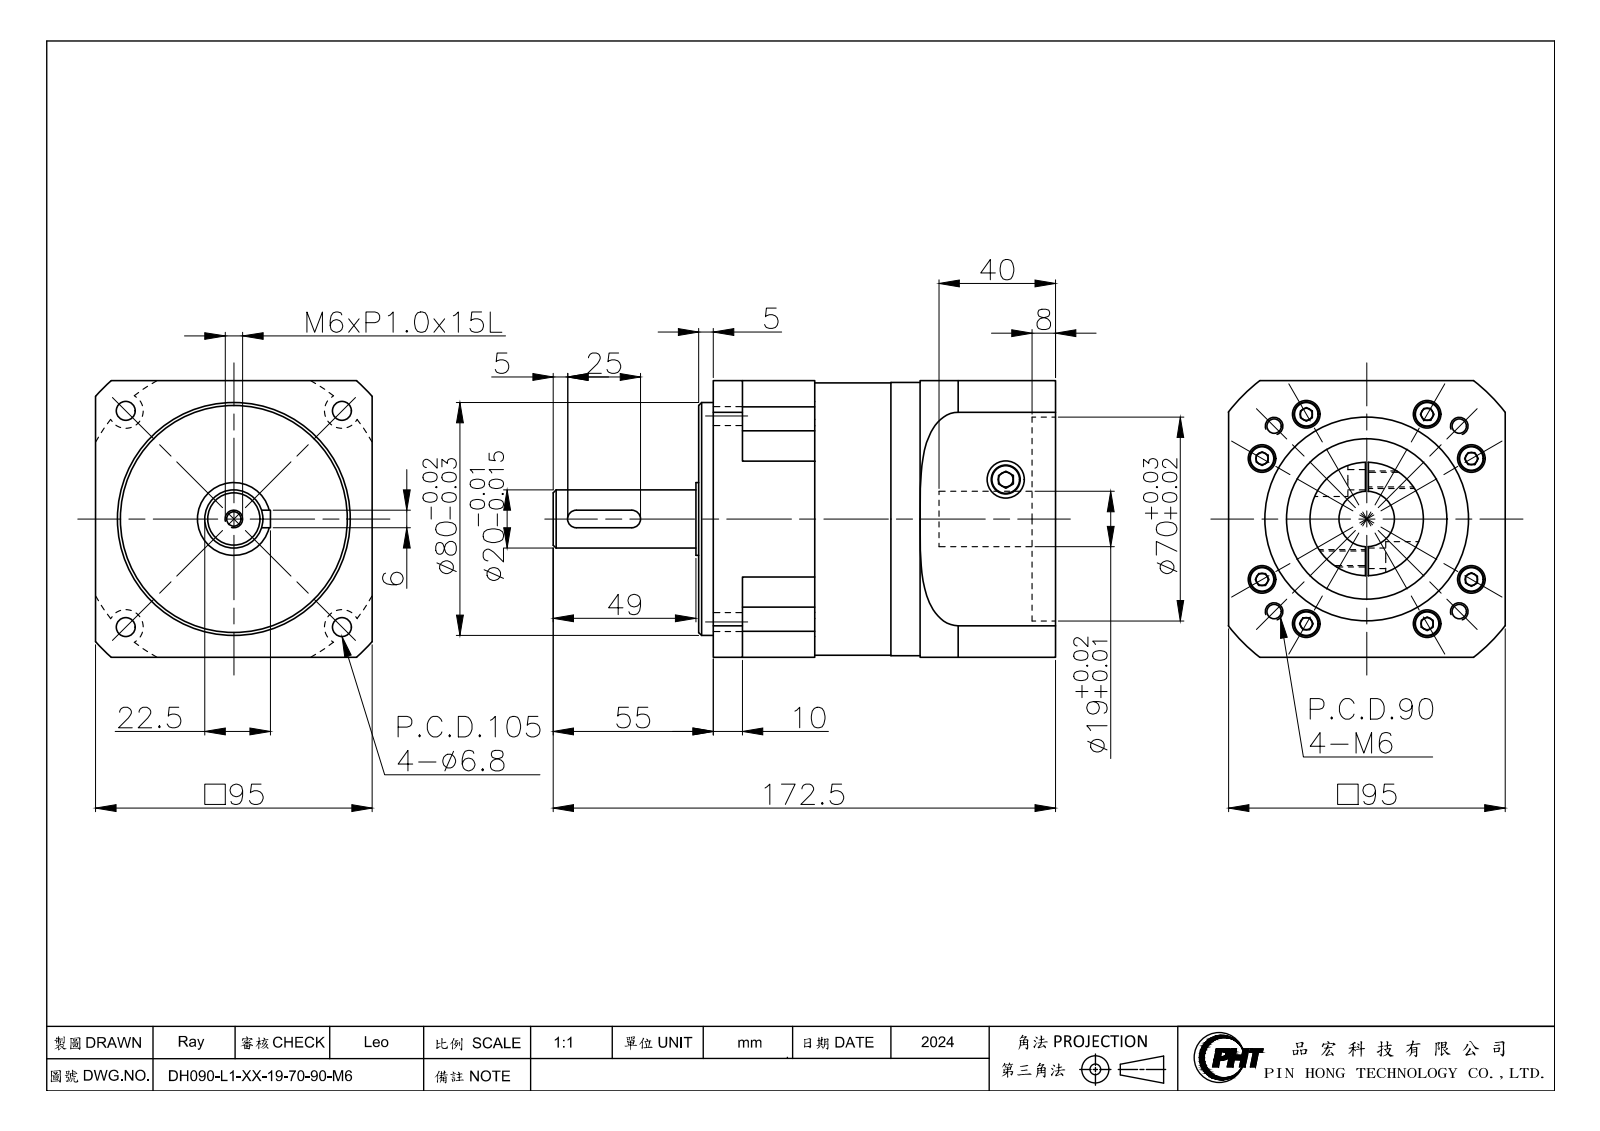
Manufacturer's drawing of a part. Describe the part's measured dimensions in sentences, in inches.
The part is named "DH090-L1-XX-19-70-90-M6_2024". Its 3-D file was written by "SolidWorks 2016 (CONFIG_CONTROL_DESIGN)". It is 1 solid with 270 faces: 125 planar, 115 cylindrical and 30 other. Overall it measures 6.791 by 3.74 by 3.74 inches. Its volume is 53.17 cubic inches and its surface area 145.8 square inches. Round holes: 8 of diameter 0.205, 8 of diameter 0.374, 5 of diameter 0.197, 4 of diameter 0.268, 2 of diameter 0.5, 1 of diameter 0.748, 1 of diameter 2.165, 1 of diameter 2.756. Round bosses or shafts: 8 of diameter 0.335, 1 of diameter 3.693, 1 of diameter 3.681, 1 of diameter 3.15, 1 of diameter 1.535, 1 of diameter 0.984, 1 of diameter 0.787. Partial cylindrical surfaces (rounded edges, fillets, slot ends): 4 of radius 0.236, 2 of radius 0.118, 1 of radius 2.047, 1 of radius 2.362, 1 of radius 2.5. The main face-to-face distances are 3.74, 4.823, 0.197, 4.626, 0.315, 1.26, 0.039, 4.508, 1.575, 3.051. The hole center spacings are 1.634, 0.465, 0.646, 2.076, 2.279, 2.311, 2.703, 2.722.
